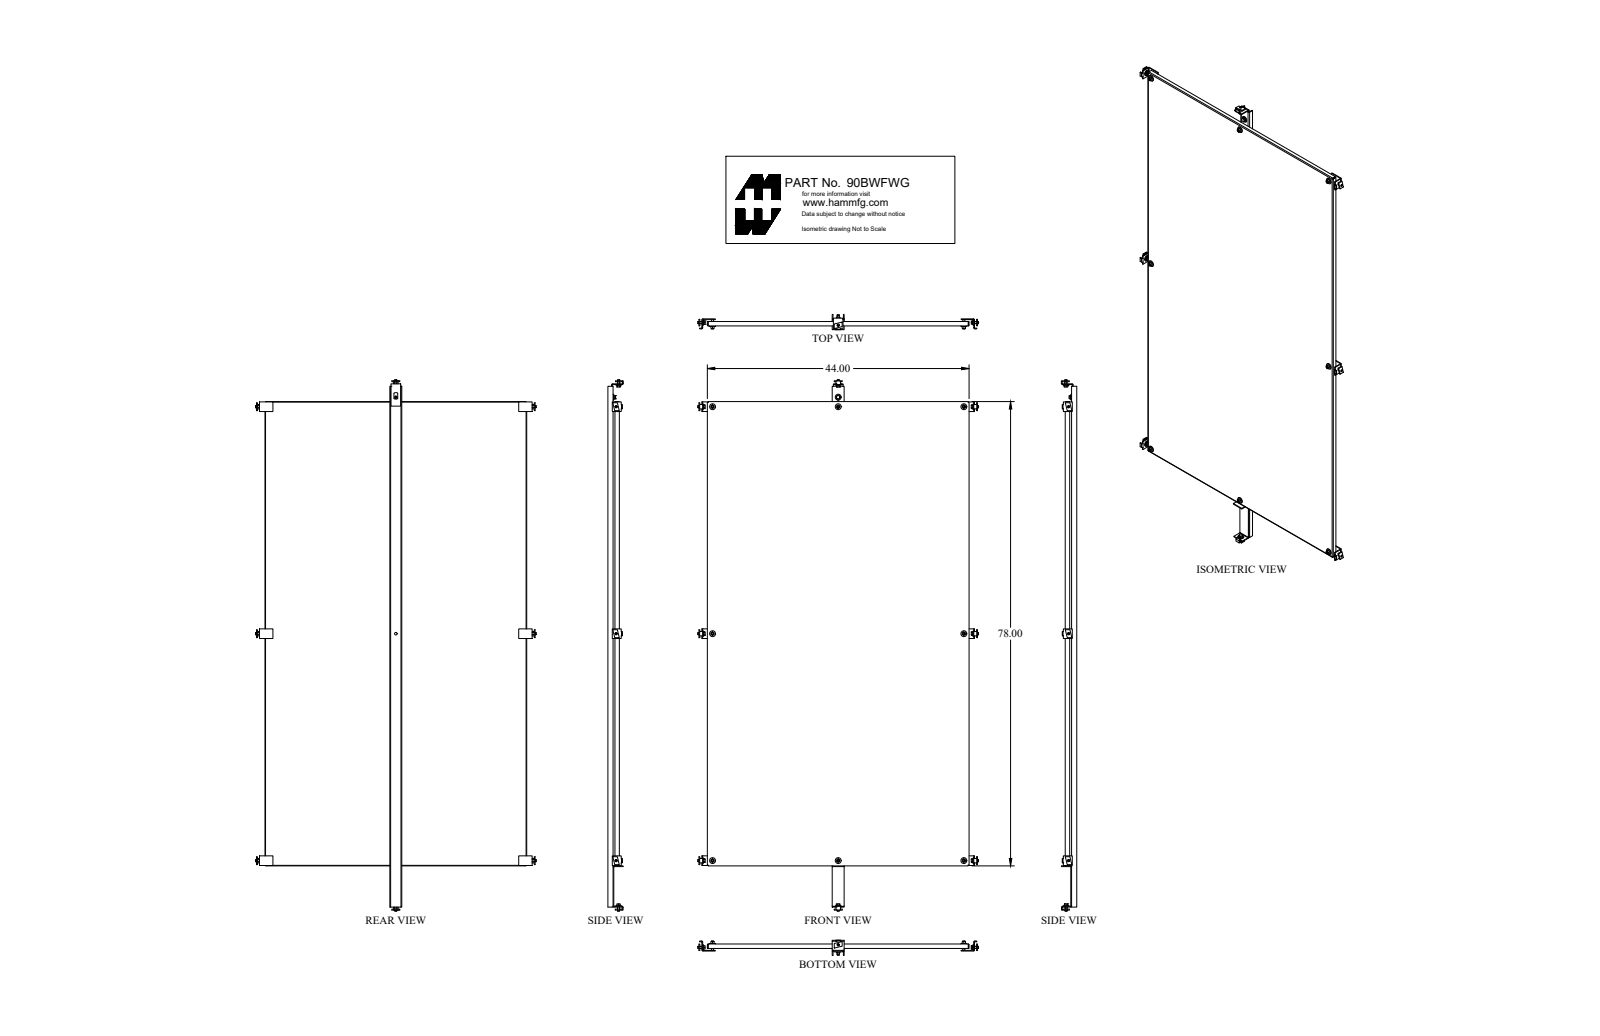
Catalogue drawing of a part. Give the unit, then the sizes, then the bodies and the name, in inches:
Units: inches
Overall size (bounding box): 88.906 × 46.582 × 2.593
Round holes (diameter × count): ⌀0.563 ×8, ⌀0.437 ×6, ⌀0.437 ×1, ⌀0.453 ×1
Round bosses / shafts (diameter × count): ⌀0.65 ×8, ⌀0.33 ×8, ⌀0.375 ×5, ⌀0.375 ×3
Partial cylindrical surfaces — rounded edges, fillets, slot ends (radius × count): R0.06 ×11, R0.185 ×11, R0.048 ×4, R0.143 ×4, R0.219 ×2
Main face-to-face distances: 0.095, 0.125, 1.187, 1.062, 0.967, 1.092, 21, 23, 20.905, 22.905
Hole centre spacings: 43.586, 43.587, 21.125, 21.125, 38.125, 38.125, 42.25, 76.25
Volume: 386.6 in³ · Surface area: 7 964 in²
Bodies: 18 solids, 385 faces (188 planar, 133 cylindrical, 64 other)
Part name (STEP PRODUCT): 90BWFWG_Default
STEP written by: SolidWorks 2018 (CONFIG_CONTROL_DESIGN)
